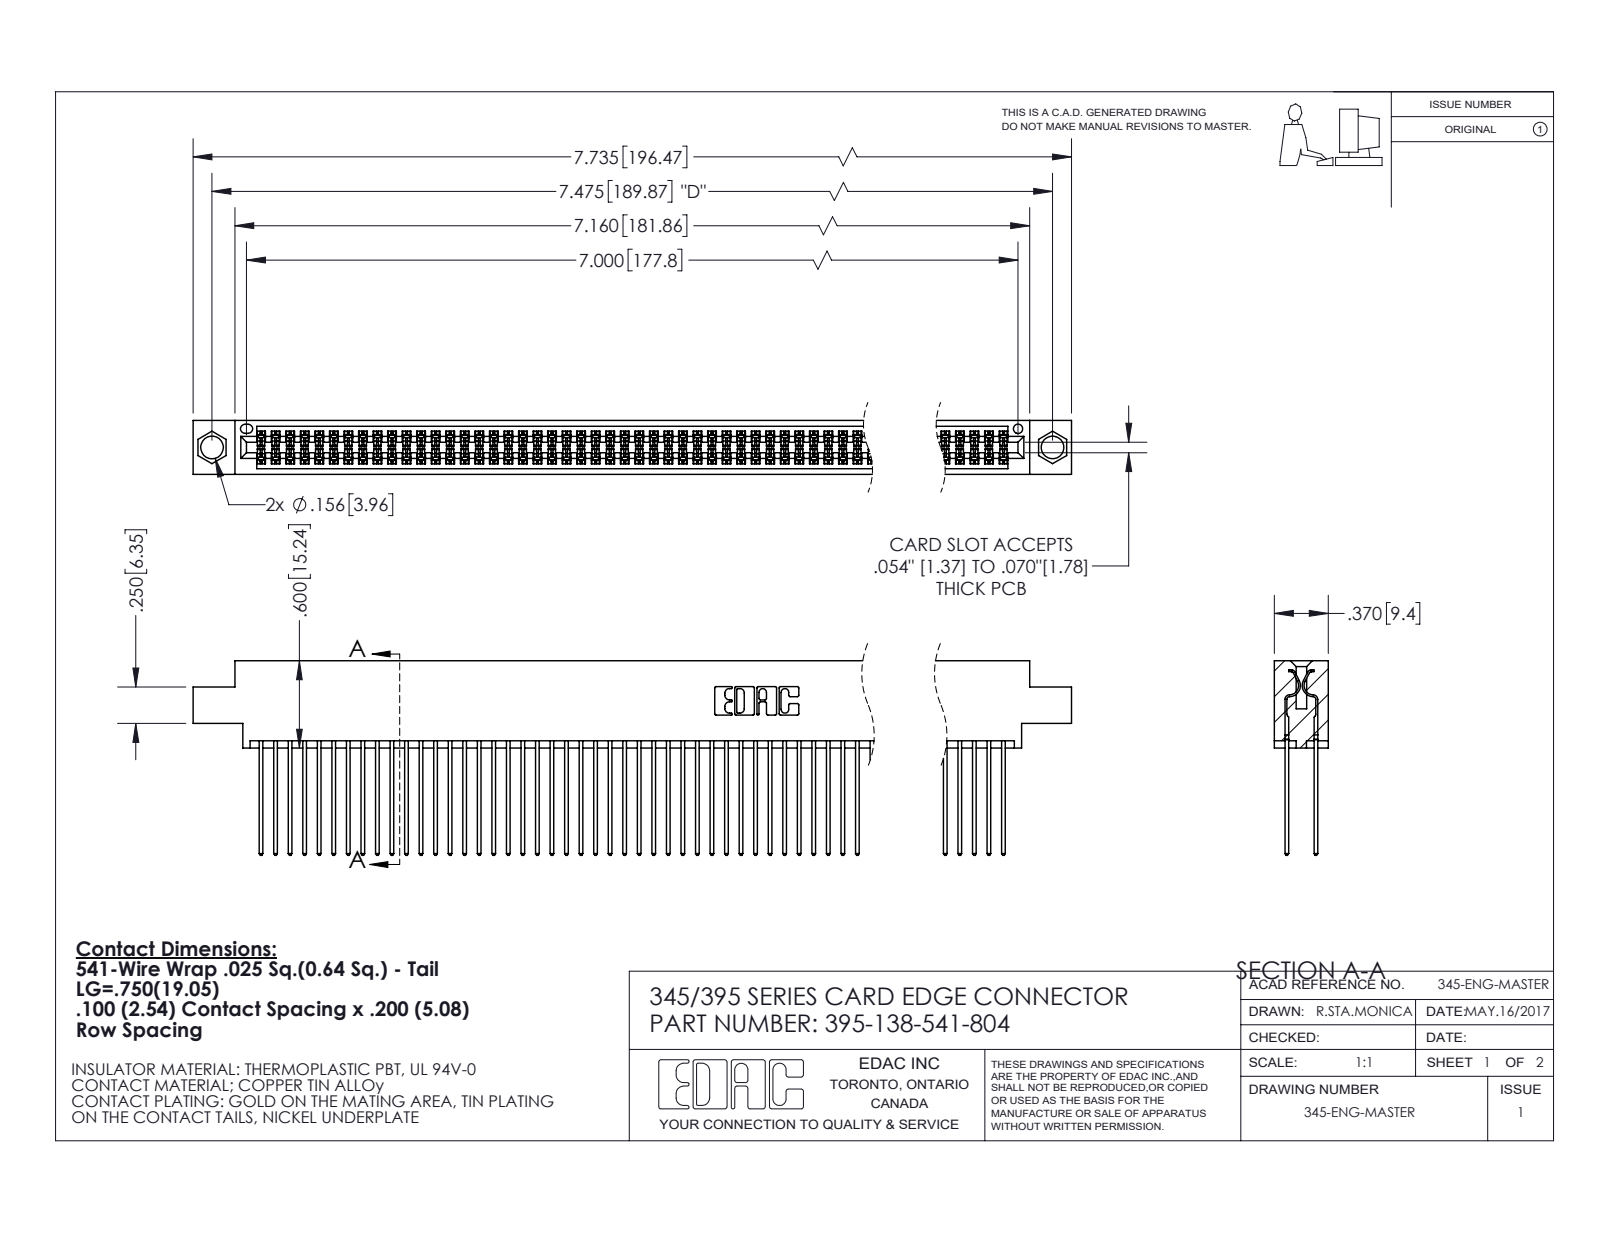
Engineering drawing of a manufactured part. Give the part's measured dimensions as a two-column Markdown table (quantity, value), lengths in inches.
| quantity | value |
| --- | --- |
| part name | 345-292-001_345-293-141; 395-138-541-804; 345 Part_0.170 Offset - 0.156 Dia-TI |
| STEP written by | SolidWorks 2020 (CONFIG_CONTROL_DESIGN) |
| units | inches |
| bodies | 139 solids, 7044 faces (4652 planar, 2392 cylindrical, 0 other) |
| overall size | 7.735 × 1.337 × 0.37 |
| volume | 1.215 in³ |
| surface area | 52.18 in² |
| round holes (diameter × count) | 0.156 × 2, 0.064 × 1 |
| partial cylindrical surfaces (radius × count) | 0.006 × 207, 0.01 × 138, 0.01 × 22, 0.007 × 6, 0.031 × 6, 0.026 × 3, 0.014 × 2, 0.019 × 2 |
| main face-to-face distances | 0.072, 0.298, 0.2, 0.098, 0.272, 0.025, 0.225, 0.37, 0.175, 0.149 |
| hole center spacings | 0.27, 7.239, 7.475 |
